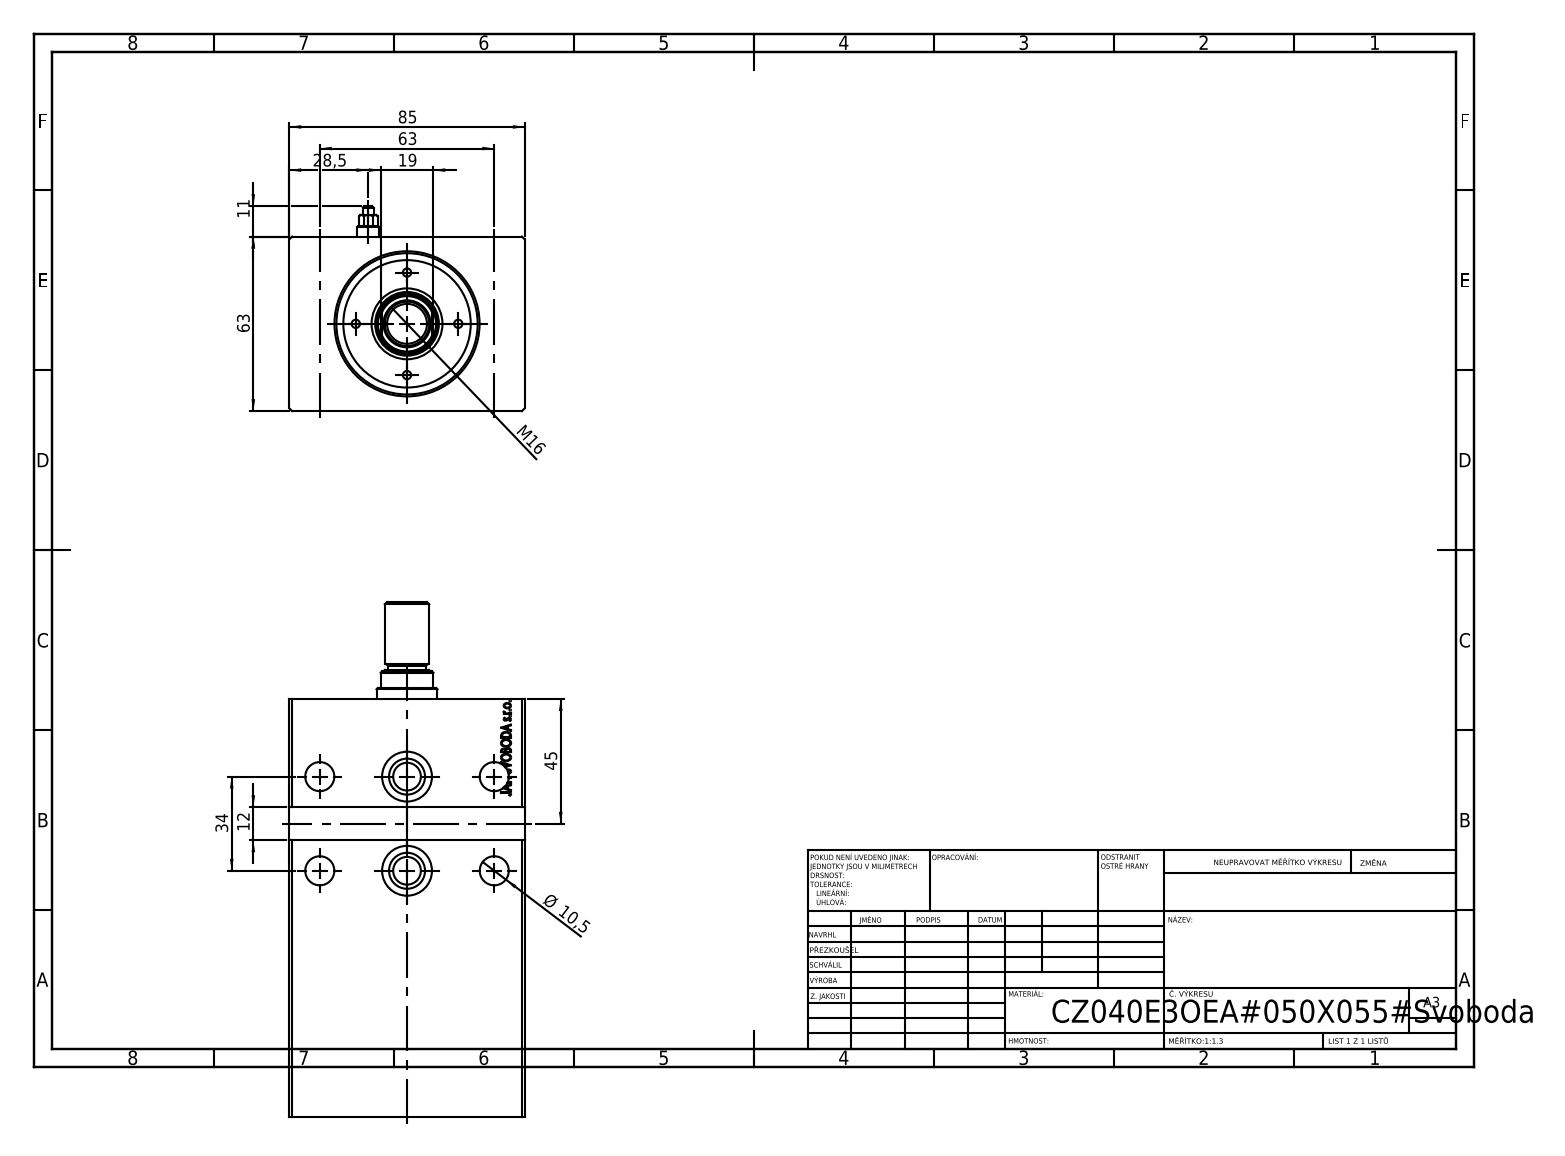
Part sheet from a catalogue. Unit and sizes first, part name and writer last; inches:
Units: inches
Overall size (bounding box): 5.945 × 3.346 × 2.48
Round holes (diameter × count): ⌀0.413 ×4, ⌀0.315 ×2, ⌀0.394 ×2, ⌀0.709 ×2, ⌀1.417 ×1, ⌀1.575 ×1, ⌀2.008 ×1
Round bosses / shafts (diameter × count): ⌀0.512 ×2
Main face-to-face distances: 2.48, 3.346, 5.945, 5.343, 0.602, 0.079, 2.402, 5.937, 0.594, 0.394
Hole centre spacings: 1.24, 1.825, 1.339, 2.48, 2.819, 0.616, 0.742, 1.197
Volume: 36.9 in³ · Surface area: 125.6 in²
Bodies: 1 solid, 779 faces (383 planar, 30 cylindrical, 366 other)
STEP written by: SolidWorks 2019 (CONFIG_CONTROL_DESIGN)
